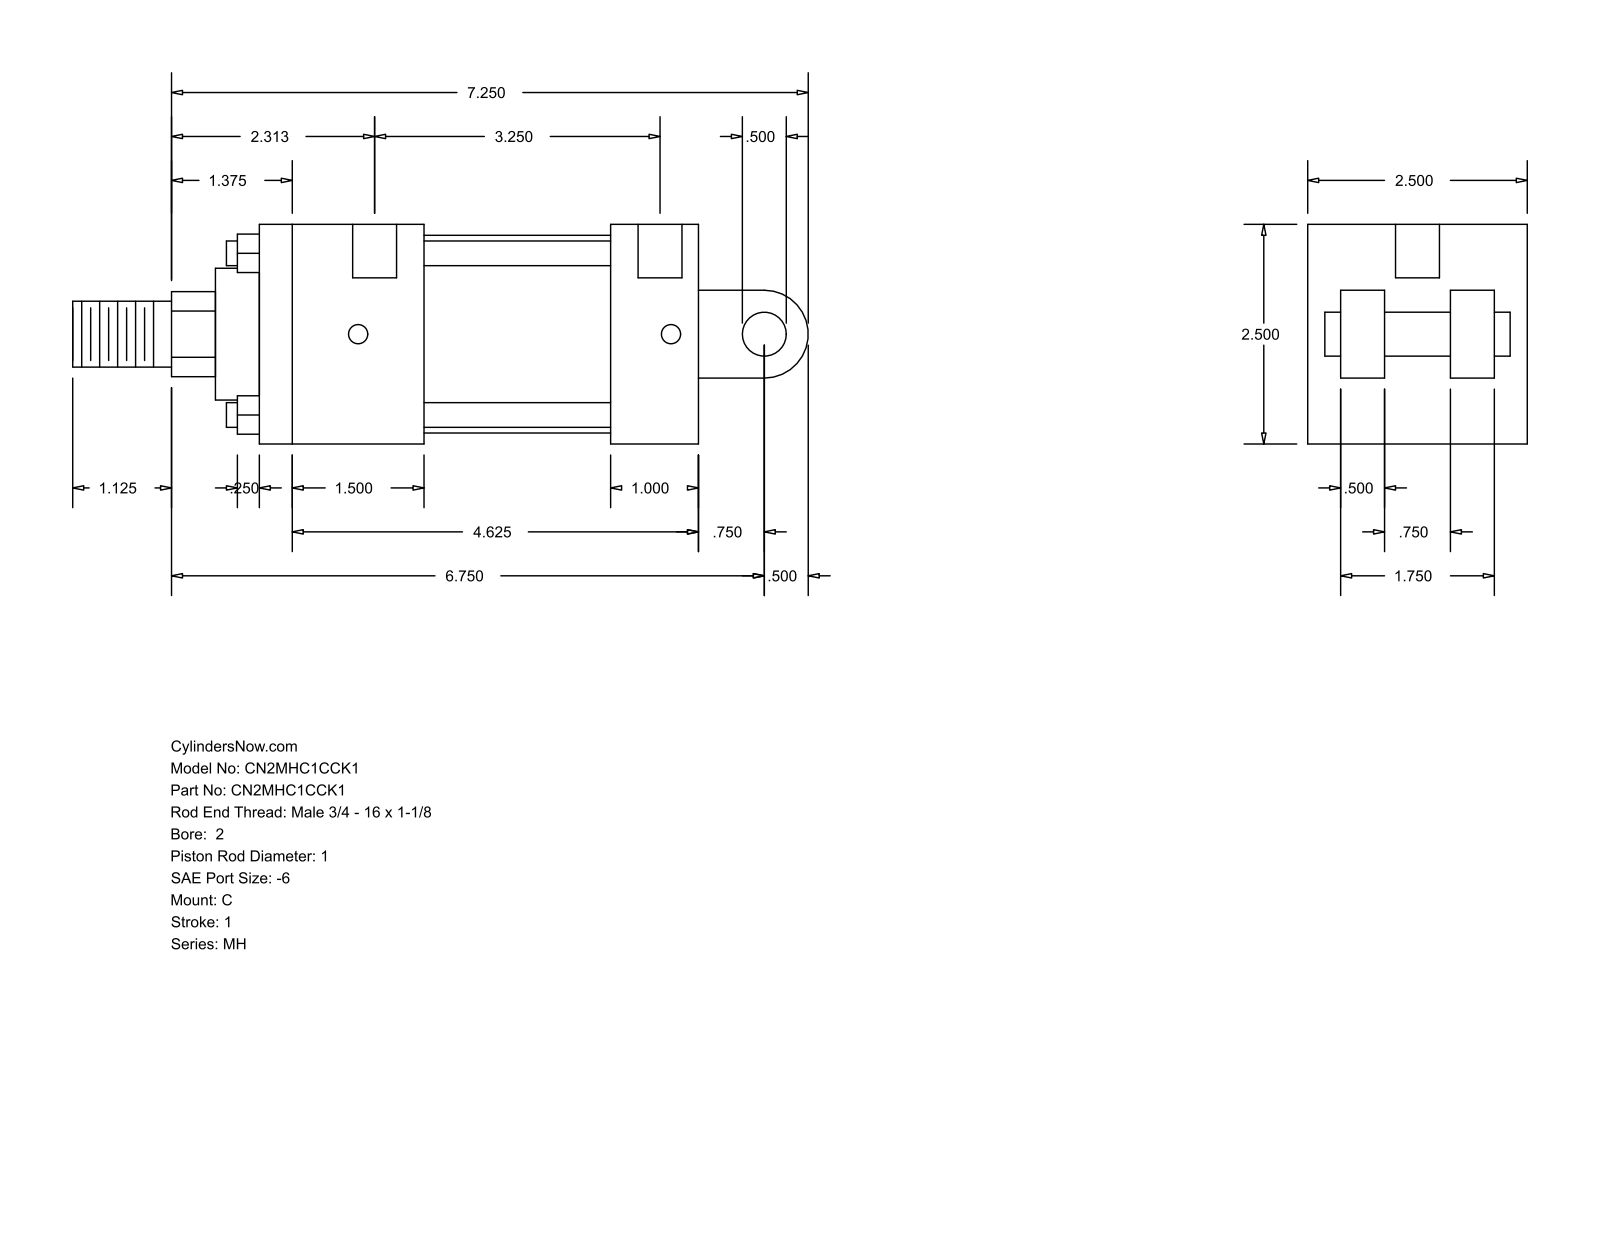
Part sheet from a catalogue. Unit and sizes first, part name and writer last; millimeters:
Units: millimetres
Overall size (bounding box): 212.72 × 63.5 × 63.5
Round holes (diameter × count): ⌀5.56 ×4, ⌀12.7 ×2
Round bosses / shafts (diameter × count): ⌀7.14 ×4, ⌀57.15 ×1, ⌀38.1 ×1, ⌀25.4 ×1, ⌀19.05 ×1, ⌀12.7 ×1
Partial cylindrical surfaces — rounded edges, fillets, slot ends (radius × count): R12.29 ×1, R12.7 ×1
Main face-to-face distances: 63.5, 127, 12.7, 25.4, 53.97, 101.6, 47.63, 53.98, 9.52, 79.37
Hole centre spacings: 90.48, 3.17, 4.76, 82.55, 85.72, 87.31
Bodies: 0 solids, 99 faces (70 planar, 29 cylindrical, 0 other)
Part name (STEP PRODUCT): MH_C__0200_1
STEP written by: GSSL Pune (CONFIG_CONTROL_DESIGN)
